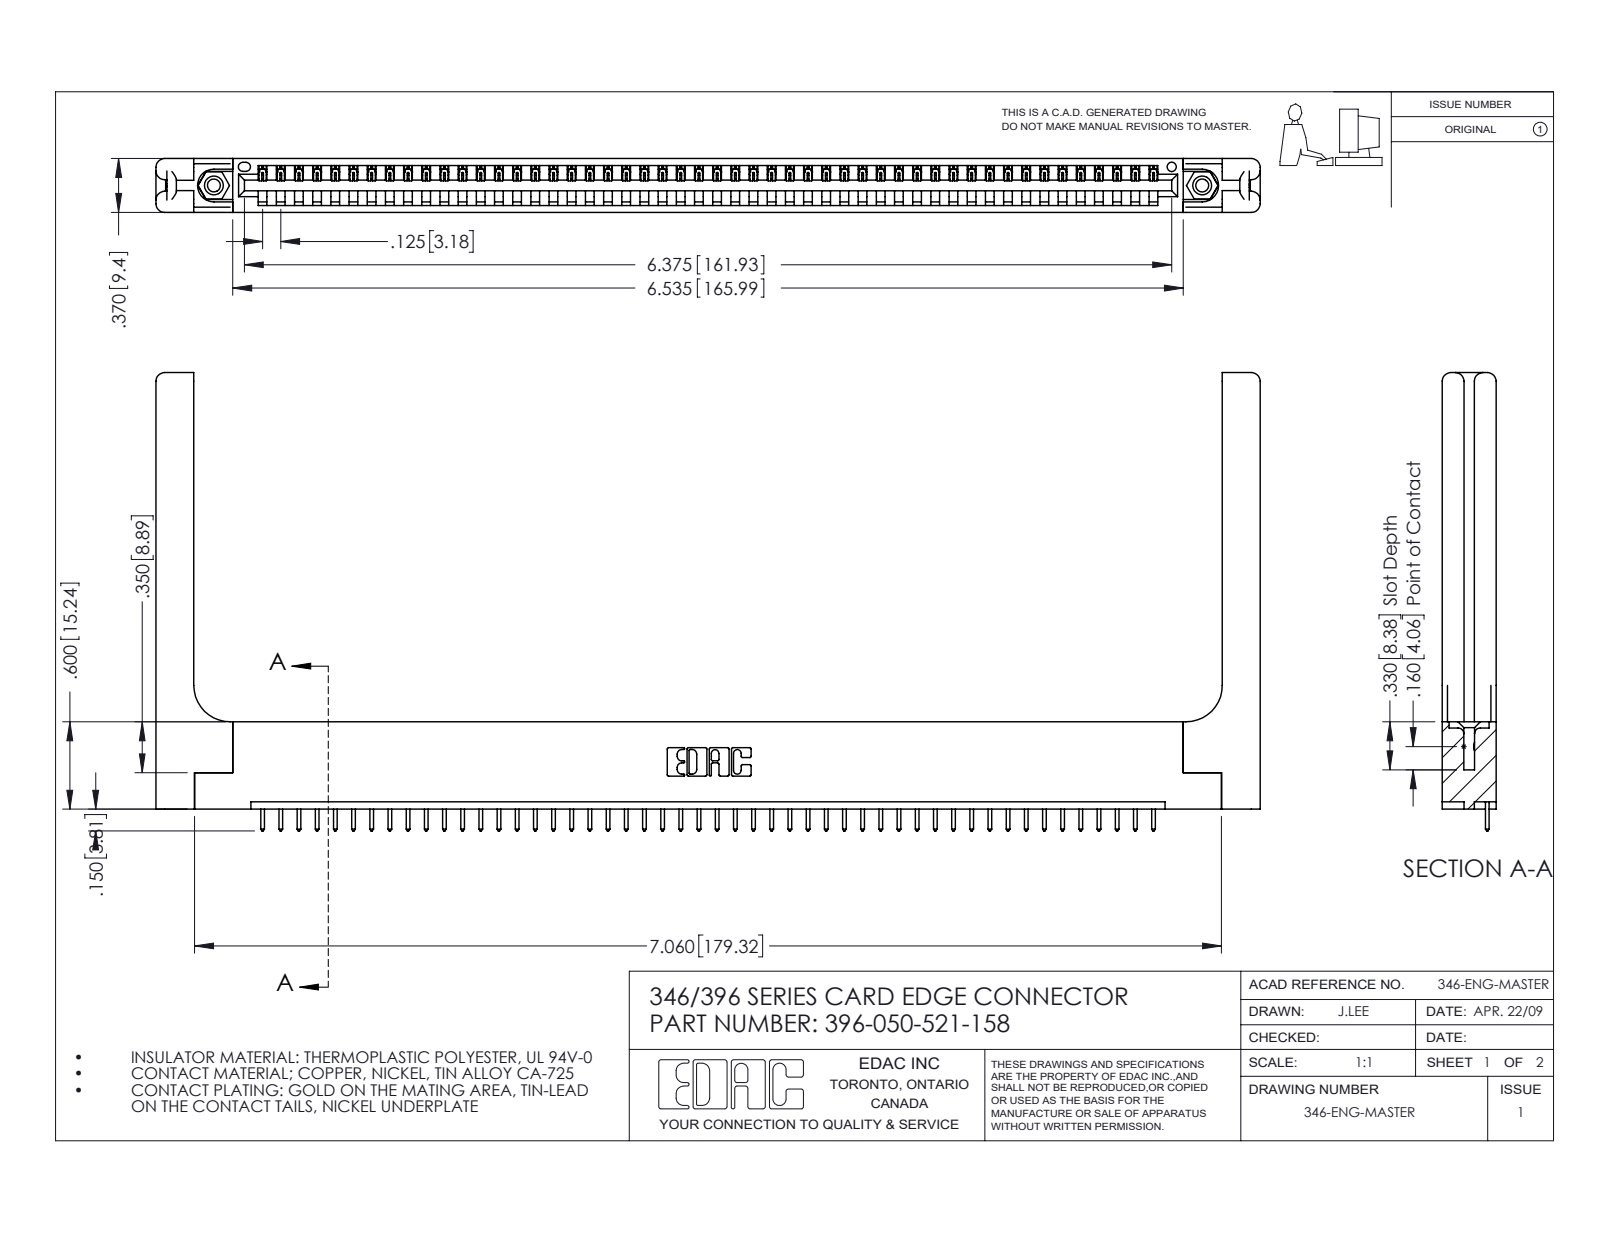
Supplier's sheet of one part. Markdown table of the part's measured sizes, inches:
| quantity | value |
| --- | --- |
| part name | 396-050-521-158; 346 Part_Flush Mounting Lugs - 0.156 Dia-TH; 345-250-001_345-250-001-102; 346-220-058_345-220-058 (+1 more) |
| STEP written by | SolidWorks 2016 (CONFIG_CONTROL_DESIGN) |
| units | inches |
| bodies | 55 solids, 3278 faces (2224 planar, 994 cylindrical, 60 other) |
| overall size | 7.591 × 3.15 × 0.37 |
| volume | 1.58 in³ |
| surface area | 42.86 in² |
| round holes (diameter × count) | 0.089 × 2, 0.125 × 2, 0.156 × 2, 0.064 × 1 |
| round bosses / shafts (diameter × count) | 0.155 × 2 |
| partial cylindrical surfaces (radius × count) | 0.006 × 100, 0.01 × 100, 0.01 × 22, 0.06 × 16, 0.007 × 6, 0.031 × 6, 0.026 × 3, 0.03 × 2 |
| main face-to-face distances | 0.37, 0.048, 0.322, 0.072, 0.148, 0.15, 0.25, 0.298, 0.025, 0.222 |
| hole center spacings | 0.246, 6.586, 6.795 |
